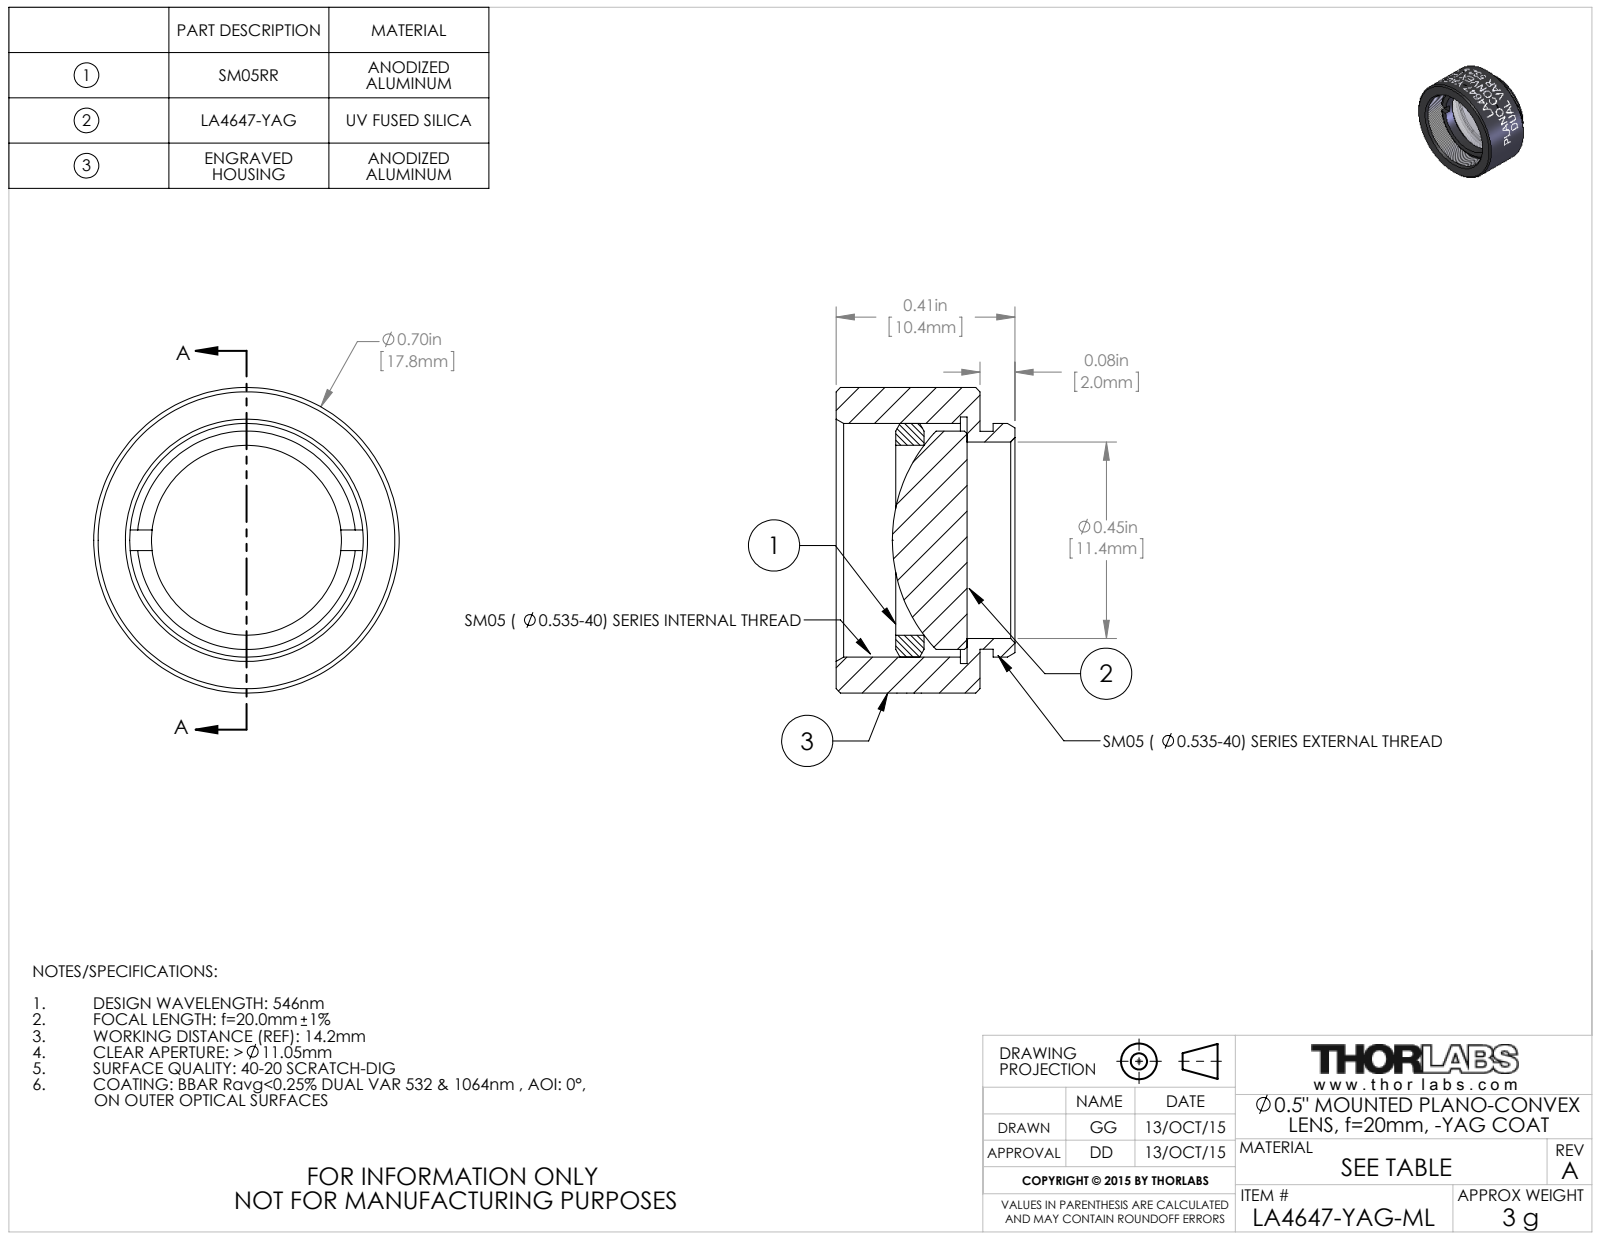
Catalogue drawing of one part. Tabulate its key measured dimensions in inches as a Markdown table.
| quantity | value |
| --- | --- |
| part name | TTN039345-E0W |
| STEP written by | SolidWorks 2014 (CONFIG_CONTROL_DESIGN) |
| units | inches |
| bodies | 3 solids, 142 faces (16 planar, 105 cylindrical, 21 other) |
| overall size | 0.7 × 0.7 × 0.41 |
| volume | 0.087 in³ |
| surface area | 2.877 in² |
| round holes (diameter × count) | 0.435 × 1, 0.45 × 1, 0.535 × 1, 0.565 × 1 |
| round bosses / shafts (diameter × count) | 0.7 × 1, 0.535 × 1, 0.5 × 1, 0.499 × 1 |
| main face-to-face distances | 0.03, 0.33, 0.3, 0.128, 0.098, 0.202, 0.193, 0.163, 0.065, 0.137 |
